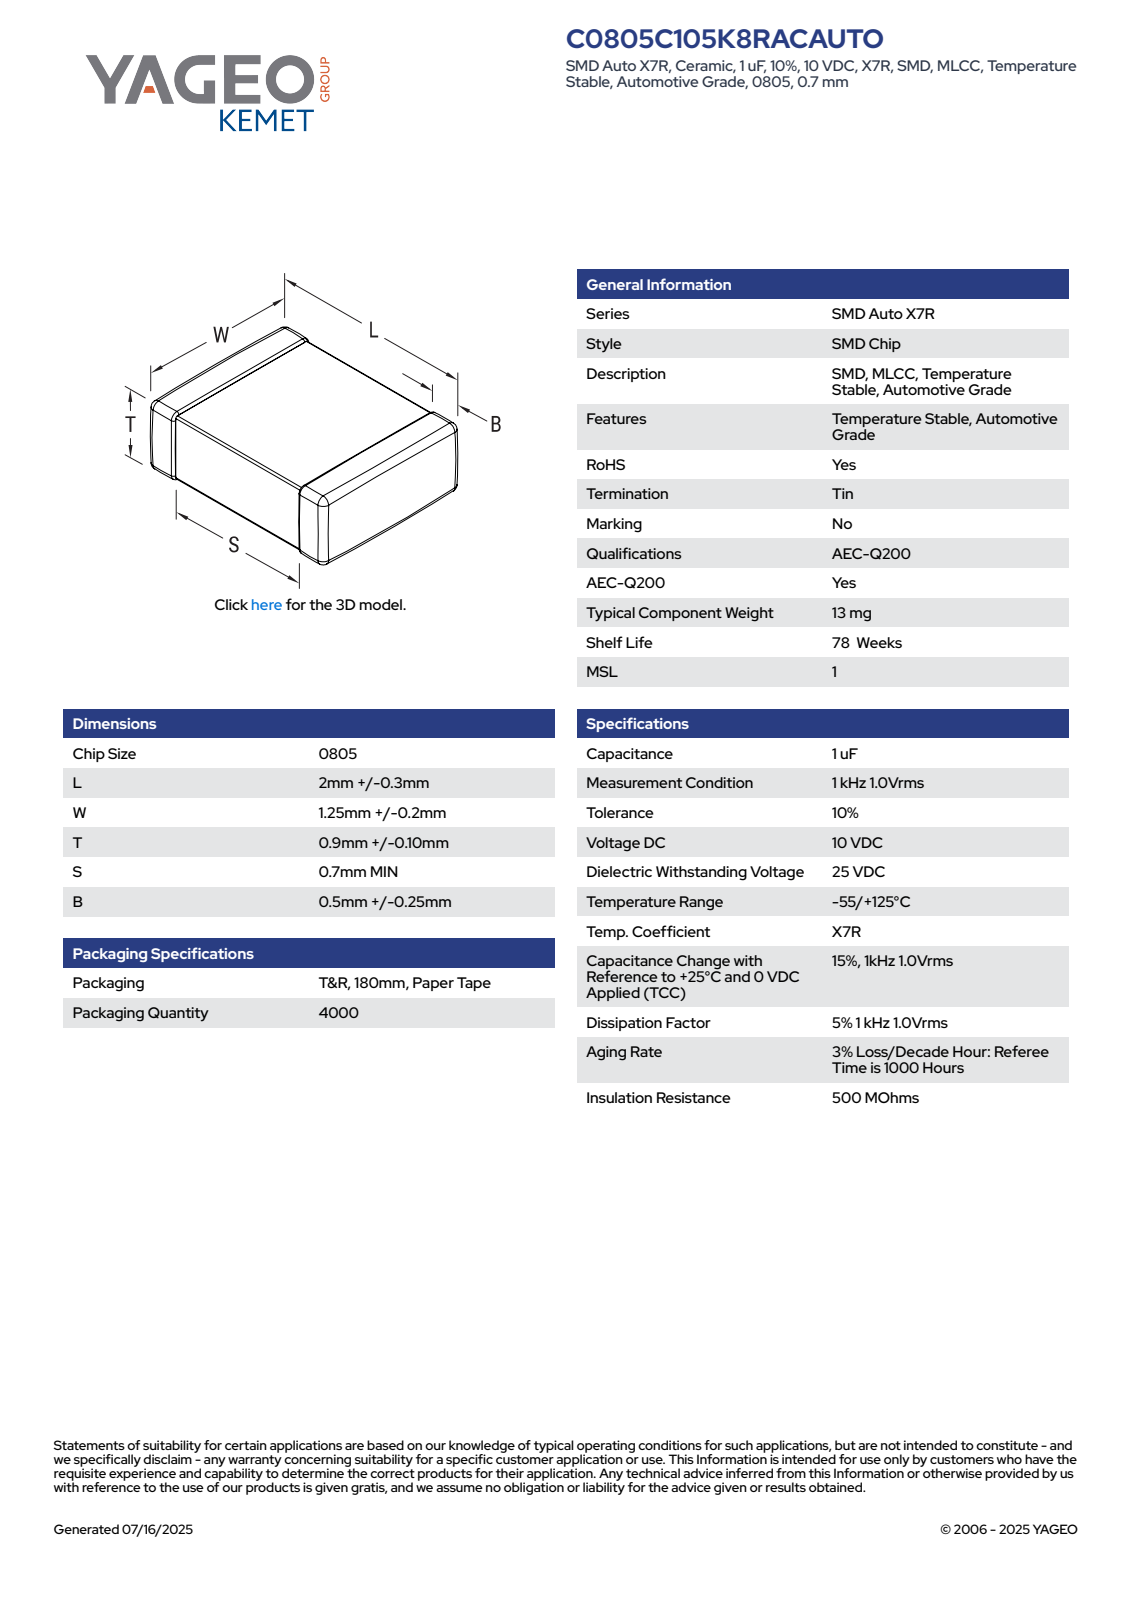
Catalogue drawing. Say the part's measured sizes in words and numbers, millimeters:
The part is named "CCS_CCSTD_0805_L2.3W1.45T1B0.5". Its 3-D file was written by "SolidWorks 2014 (AUTOMOTIVE_DESIGN)". It is 4 solids with 125 faces: 71 planar, 38 cylindrical and 16 other. Overall it measures 2.3 by 1.45 by 1 millimeters. Its volume is 3 cubic millimeters and its surface area 14 square millimeters. The main face-to-face distances are 0.97, 0.94, 1.42, 2.3, 1, 1.39, 1.45, 1.03, 1.27, 1.24.
